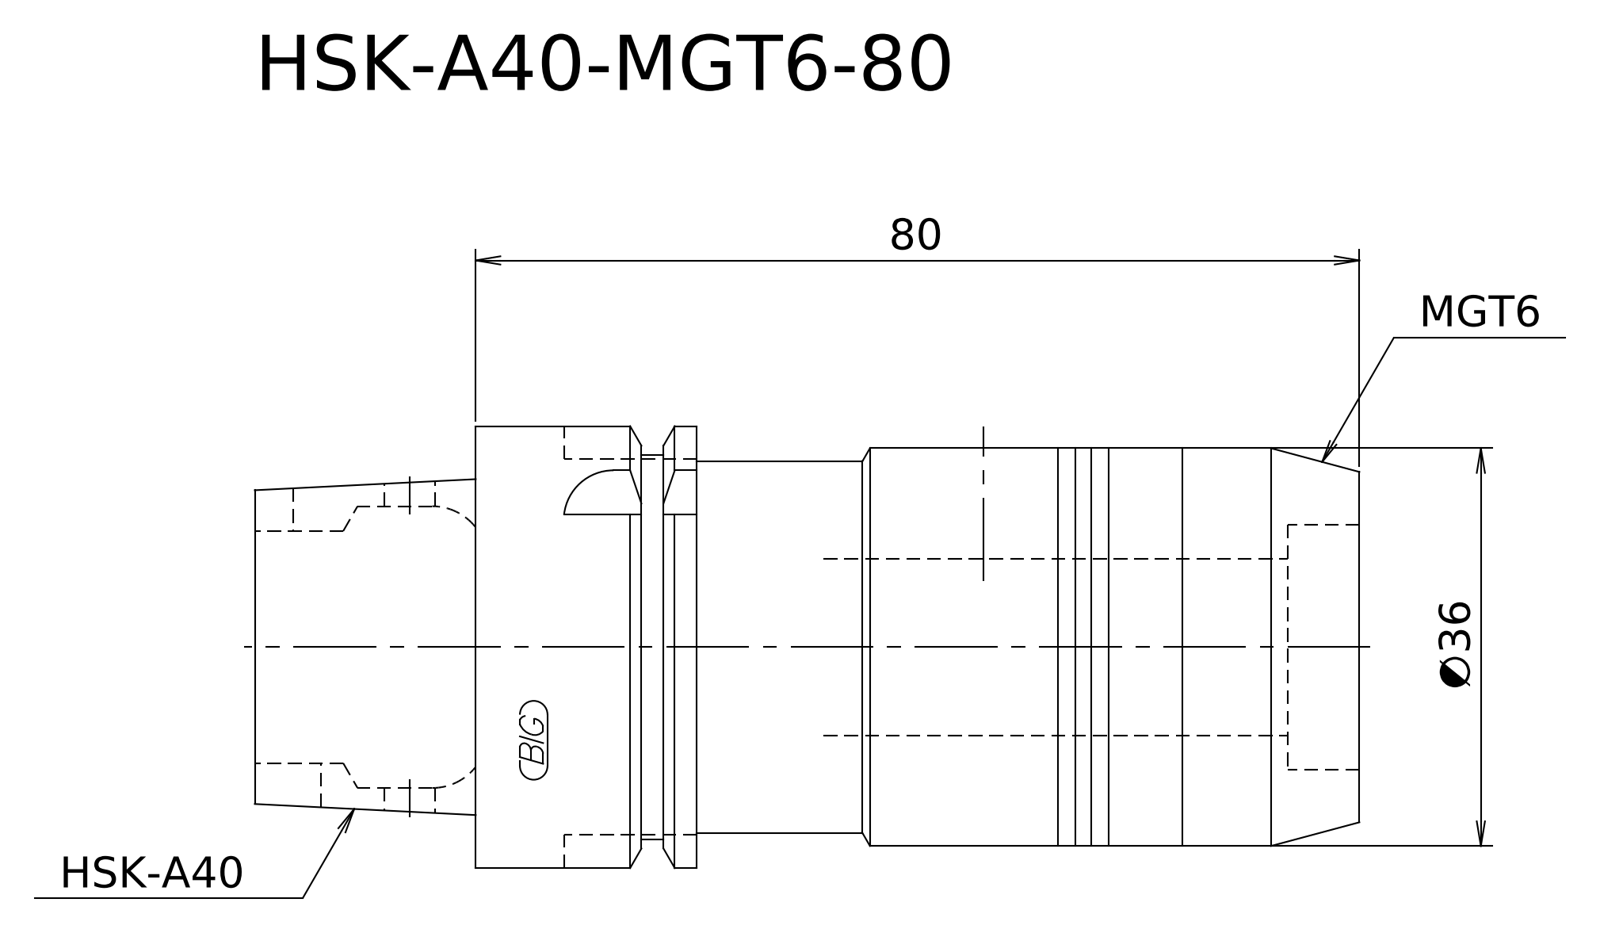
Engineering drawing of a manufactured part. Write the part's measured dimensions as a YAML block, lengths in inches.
step_written_by: "Kubotek KeyCreator V8.5.1 (14335) (CONFIG_CONTROL_DESIGN)"
units: inches
bodies: {solids: 1, faces: 17, planar: 6, cylindrical: 6, other: 5}
overall_size: [3.937, 1.575, 1.575]
volume: 5.858
surface_area: 21.4
round_bosses_or_shafts:
  - {diameter: 1.575, count: 1}
  - {diameter: 1.417, count: 1}
  - {diameter: 1.37, count: 1}
  - {diameter: 1.323, count: 1}
  - {diameter: 1.189, count: 1}
face_to_face_distances: [0.787, 3.937, 3.15, 2.362, 1.575, 2.559, 0.197, 0.591, 1.378, 2.48]
